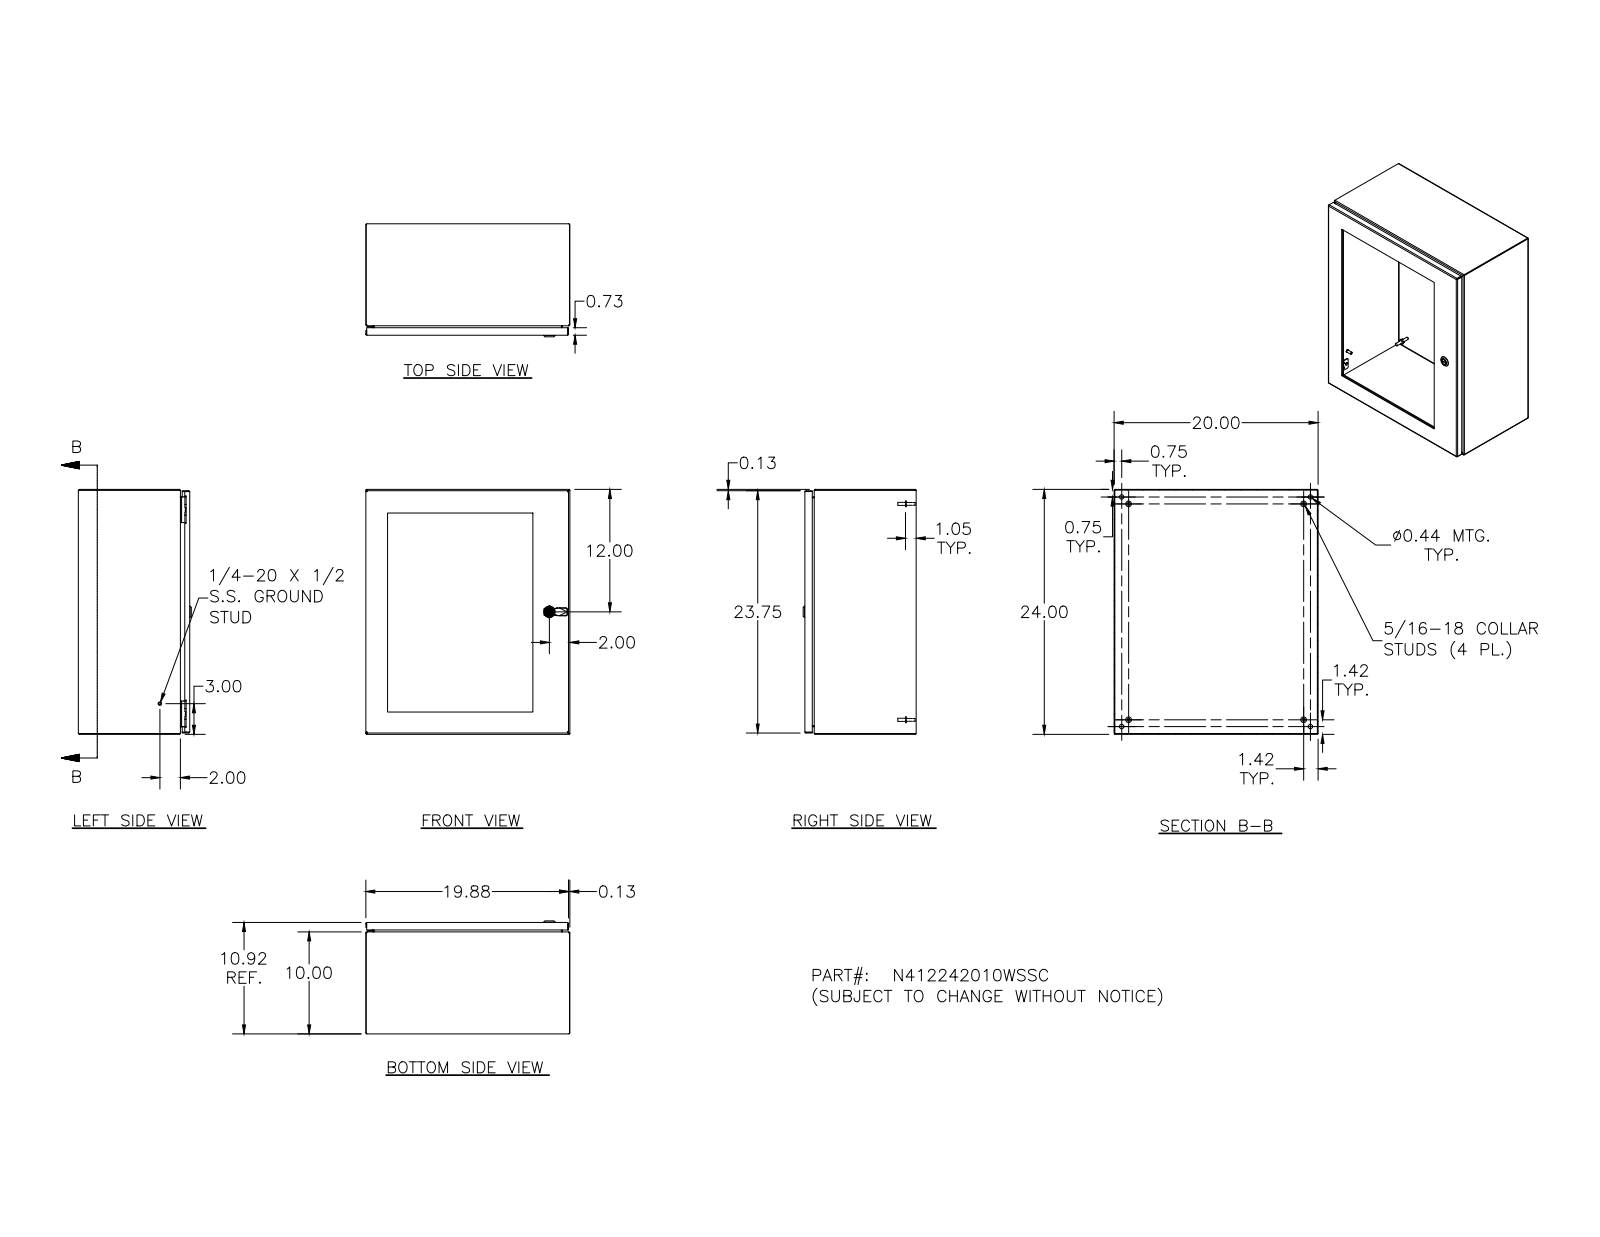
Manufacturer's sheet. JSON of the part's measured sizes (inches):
{"part_name": "N412242010WSSC; N412242010WSSCBKP; N4122420WSSCLID; HFW328176 (+8 more)", "step_written_by": "Autodesk Inventor 2011 (AUTOMOTIVE_DESIGN)", "units": "inches", "bodies": {"solids": 74, "faces": 2004, "planar": 776, "cylindrical": 573, "other": 655}, "overall_size": [24, 20, 11.075], "volume_in3": 212.8, "surface_area_in2": 4323, "round_holes": [[0.156, 20], [0.281, 18], [0.093, 4], [0.152, 4], [0.167, 4], [0.172, 4], [0.188, 4], [0.437, 4], [0.187, 1], [0.197, 1], [0.315, 1], [0.394, 1]], "round_bosses_or_shafts": [[0.19, 18], [0.253, 17], [0.25, 10], [0.563, 4], [0.36, 4], [0.32, 4], [0.3, 4], [0.275, 4]], "partial_cylinders_radius": [[0.031, 34], [0.05, 26], [0.105, 24], [0.016, 18], [0.125, 16], [0.02, 9], [0.032, 8], [0.157, 4]], "face_to_face_distances": [0.074, 10.843, 10.769, 19.926, 23.926, 0.25, 10.593, 10.519, 20, 19.852], "hole_center_spacings": [4, 8, 16.008, 12, 17.443, 20, 21.132, 15.5]}
